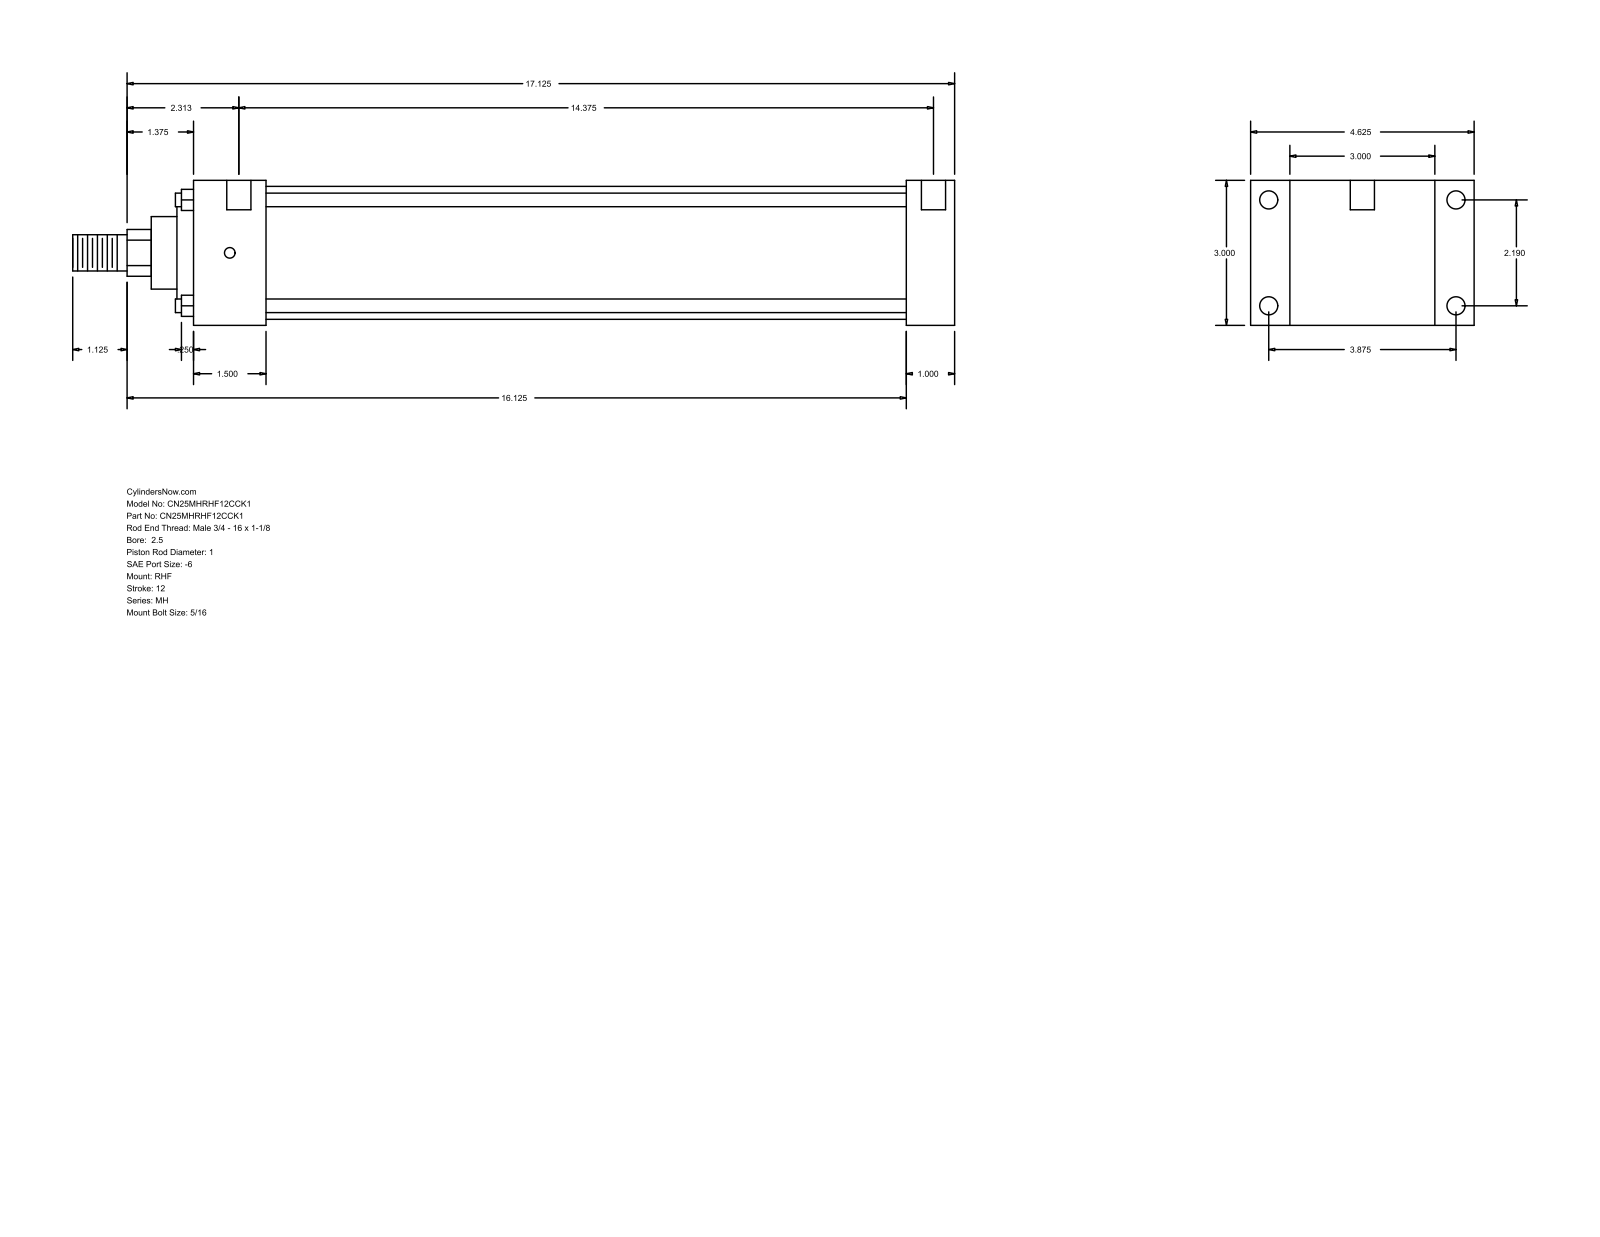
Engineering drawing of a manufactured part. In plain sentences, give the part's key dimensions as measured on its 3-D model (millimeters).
The part is named "MH_RHF__0250_1". Its 3-D file was written by "GSSL Pune (CONFIG_CONTROL_DESIGN)". It is 0 solids with 90 faces: 61 planar, 29 cylindrical and 0 other. Overall it measures 463.55 by 117.47 by 76.2 millimeters. Round holes: 4 of diameter 5.56, 4 of diameter 9.53, 2 of diameter 12.7. Round bosses or shafts: 4 of diameter 7.14, 1 of diameter 69.85, 1 of diameter 60.33, 1 of diameter 38.1, 1 of diameter 25.4, 1 of diameter 19.05. Partial cylindrical surfaces (rounded edges, fillets, slot ends): 1 of radius 12.29. The main face-to-face distances are 76.2, 25.41, 20.64, 96.84, 374.65, 400.06, 117.48, 38.11, 336.54, 361.95. The hole center spacings are 55.62, 98.42, 113.05, 373.06, 3.18, 4.76, 365.12, 368.3.
